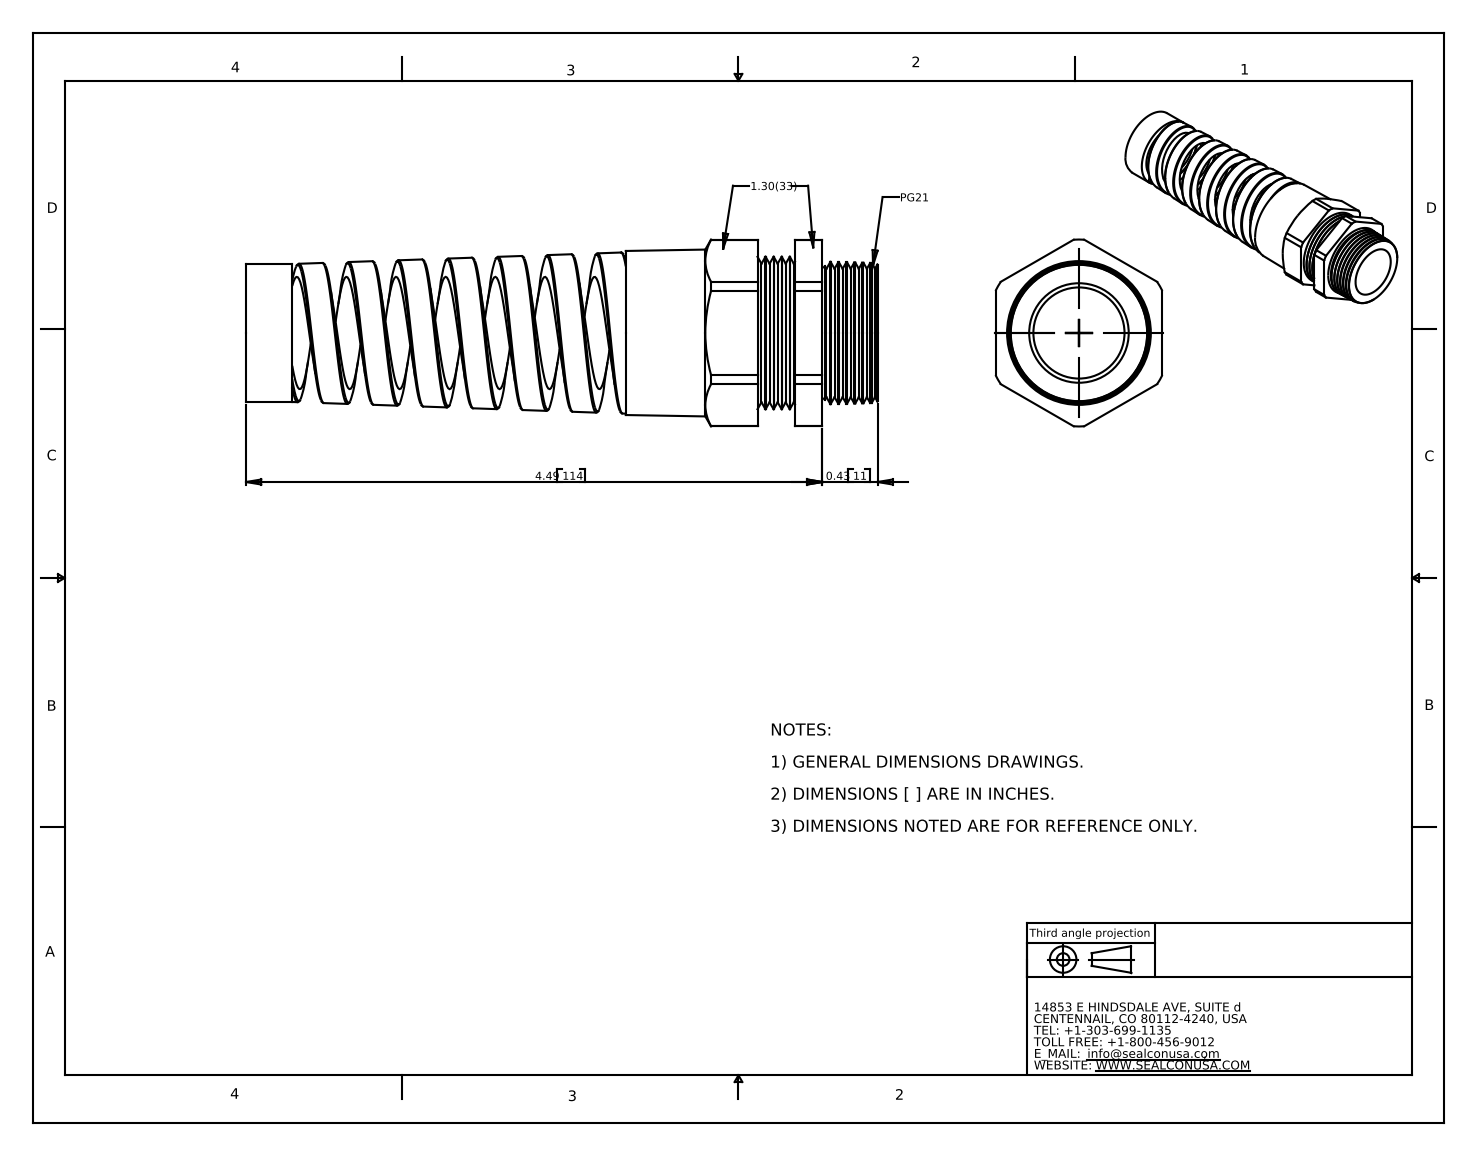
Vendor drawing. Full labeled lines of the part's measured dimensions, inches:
Part name (STEP PRODUCT): CF21AA-GY
STEP written by: SolidWorks 2007 (CONFIG_CONTROL_DESIGN)
Units: inches
Bodies: 1 solid, 157 faces (19 planar, 41 cylindrical, 97 other)
Overall size (bounding box): 4.92 × 1.456 × 1.3
Volume: 2.326 in³ · Surface area: 35 in²
Round holes (diameter × count): ⌀0.71 ×1, ⌀0.875 ×1
Round bosses / shafts (diameter × count): ⌀1.187 ×1, ⌀1.075 ×1
Partial cylindrical surfaces — rounded edges, fillets, slot ends (radius × count): R0.728 ×1
Main face-to-face distances: 1.3, 1.532, 1.962, 0.43, 1.319, 0.214, 0.644, 1.026, 0.292, 0.506
